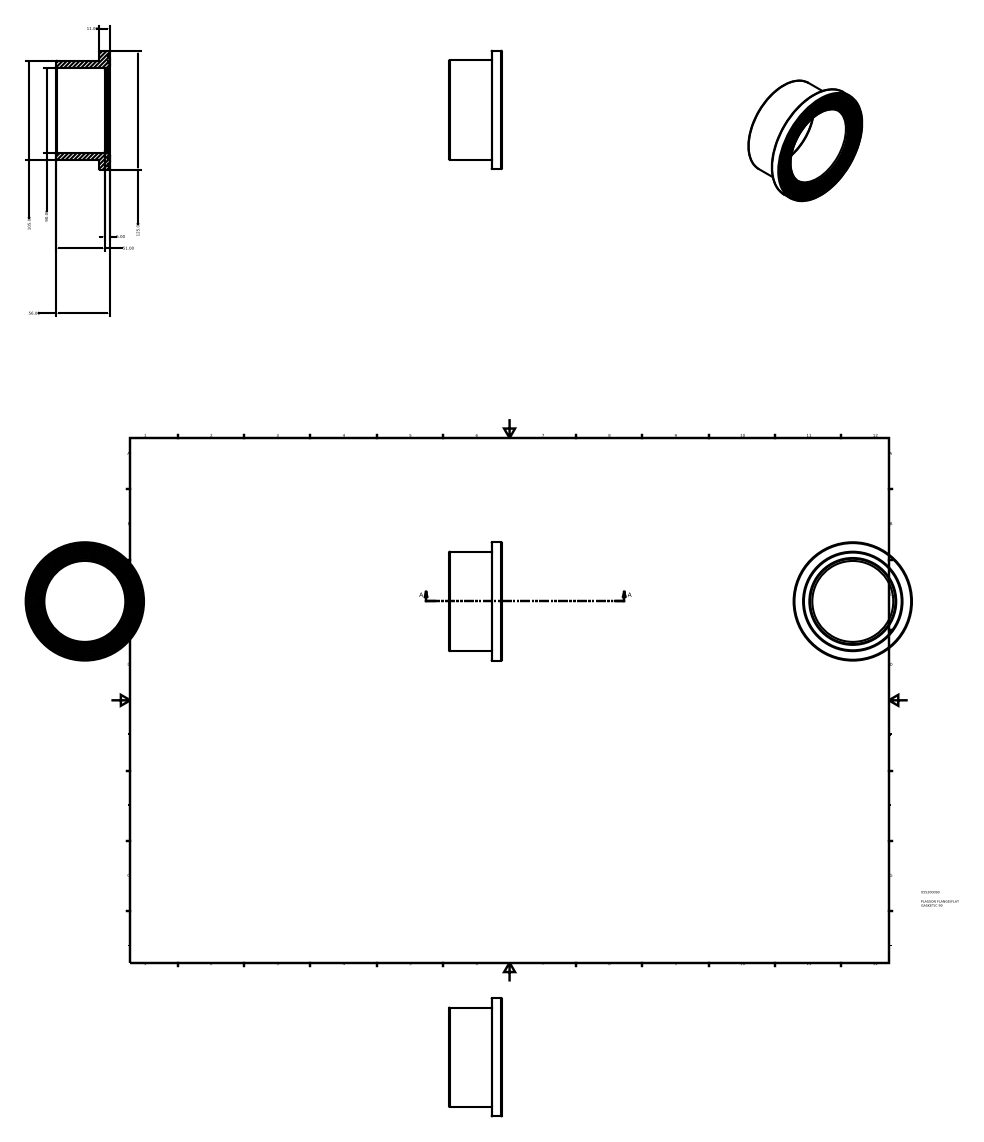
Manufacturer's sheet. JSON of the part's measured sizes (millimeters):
{"part_name": "055200090", "step_written_by": "Autodesk Inventor 2015 (AUTOMOTIVE_DESIGN)", "units": "millimeters", "bodies": {"solids": 1, "faces": 28, "planar": 9, "cylindrical": 4, "other": 15}, "overall_size": [125, 125, 56], "volume_mm3": 165711, "surface_area_mm2": 48360, "round_holes": [[85.5, 1], [90, 1]], "round_bosses_or_shafts": [[125, 1], [105, 1]], "face_to_face_distances": [45, 56, 11, 54.35, 9.35, 1.65, 51, 6, 3.35, 5]}
